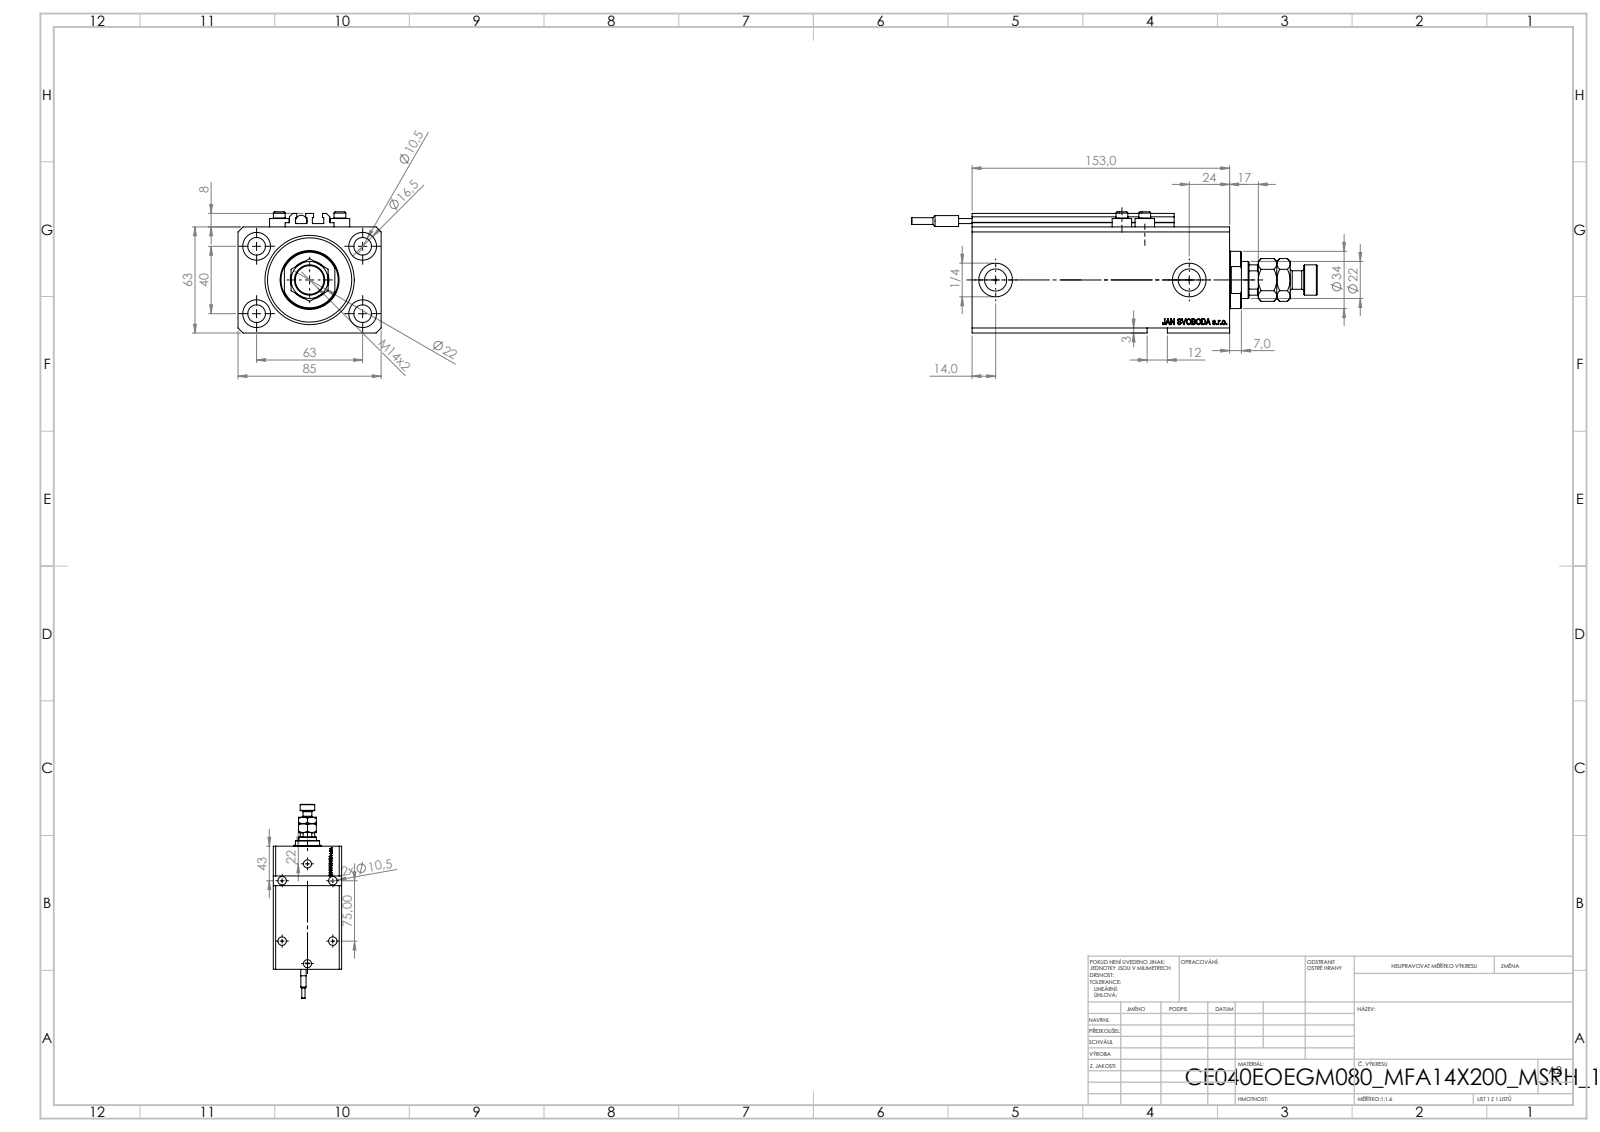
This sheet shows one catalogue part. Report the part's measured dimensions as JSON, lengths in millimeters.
{"part_name": "MFA; V250CE_E_Body; SWITCH_V250CE; V250CE_VC_E (+2 more)", "step_written_by": "SolidWorks 2019 (CONFIG_CONTROL_DESIGN)", "units": "millimeters", "bodies": {"solids": 10, "faces": 1185, "planar": 567, "cylindrical": 156, "other": 462}, "overall_size": [241, 85, 72], "volume_mm3": 696323, "surface_area_mm2": 145428, "round_holes": [[10.5, 8], [1.25, 4], [4, 4], [16.5, 4], [10, 2], [13.16, 2], [20, 2], [12.5, 1], [22, 1], [40, 1], [53, 1]], "round_bosses_or_shafts": [[11.6, 4], [7, 4], [34, 1], [18, 1], [11, 1], [6.8, 1], [6.5, 1], [4, 1]], "partial_cylinders_radius": [[0.2, 10], [10.5, 1]], "face_to_face_distances": [63, 85, 17, 153, 136, 11.4, 124.6, 141.6, 65, 3], "hole_center_spacings": [37.31, 63, 13.6, 15.4, 24.96, 33.62, 36, 37.86]}
